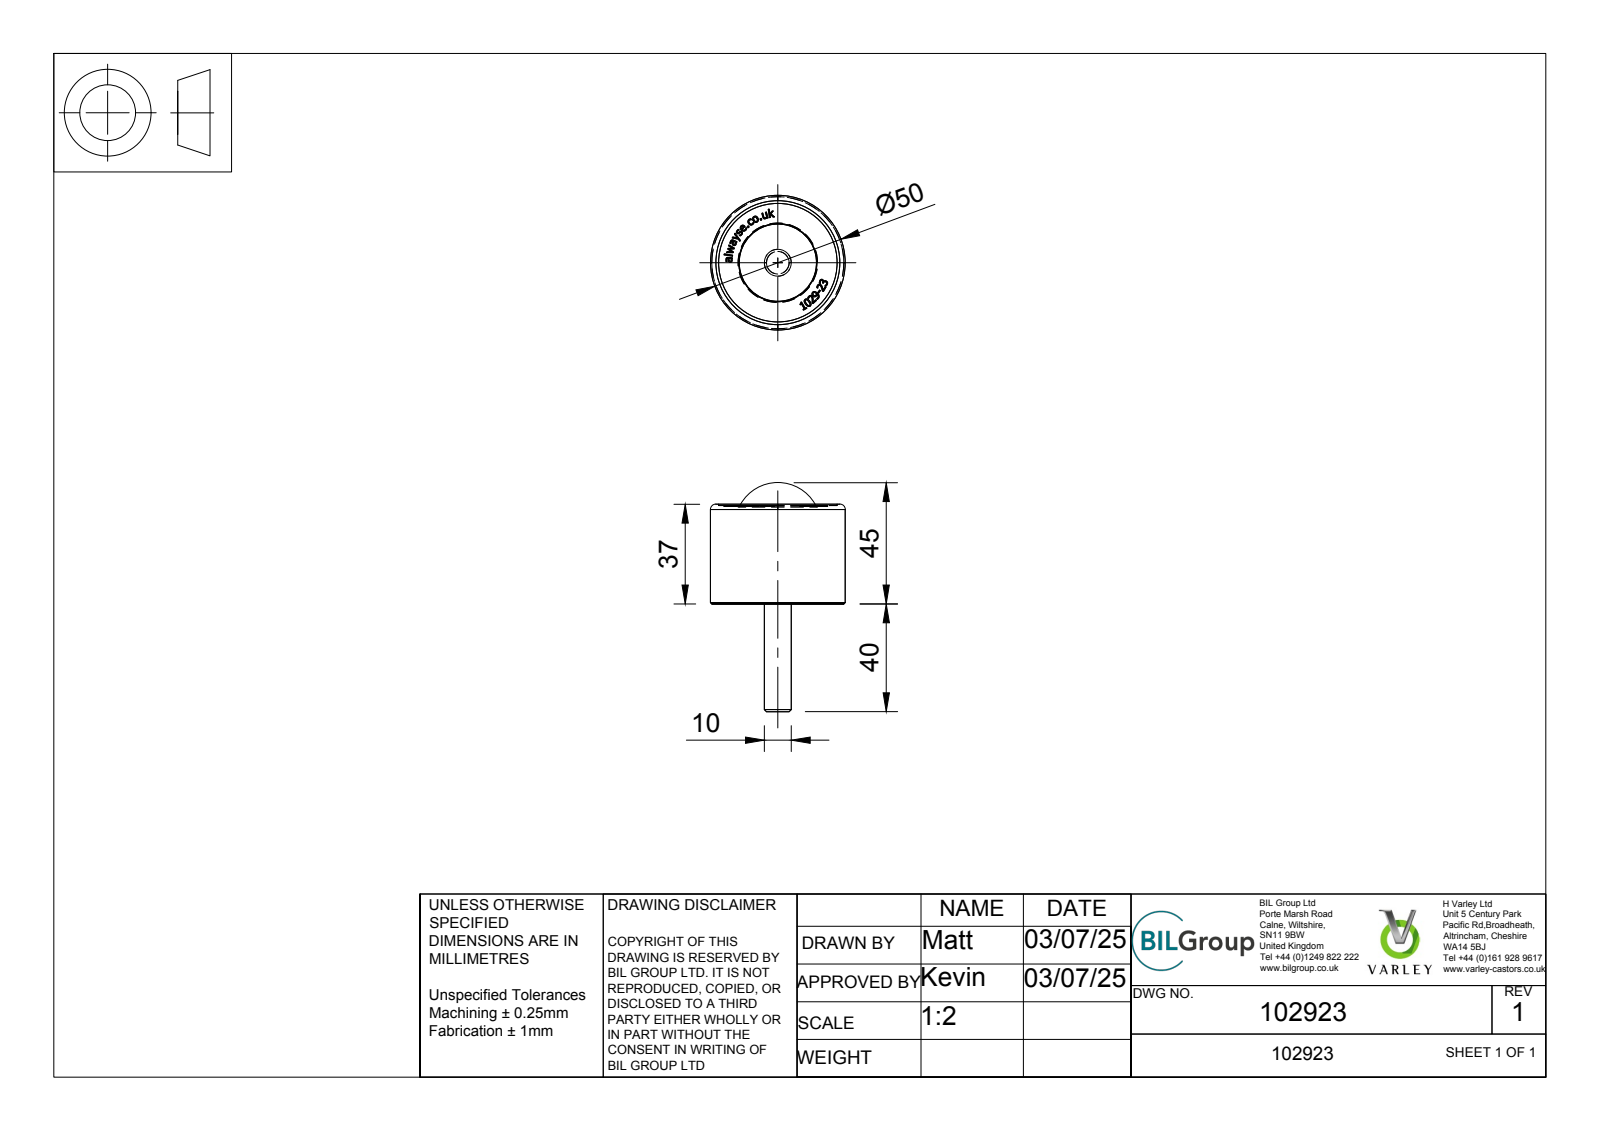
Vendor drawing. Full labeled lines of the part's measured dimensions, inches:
Part name (STEP PRODUCT): 102923 v1; 102923
STEP written by: Autodesk Translation Framework v14.10.0.0 (AUTOMOTIVE_DESIGN)
Units: inches
Bodies: 0 solids, 322 faces (147 planar, 6 cylindrical, 169 other)
Overall size (bounding box): 3.346 × 1.969 × 1.969
Round bosses / shafts (diameter × count): ⌀1.969 ×1, ⌀1.732 ×1, ⌀0.394 ×1
Main face-to-face distances: 1.437, 0.02, 1.457, 1.575, 3.012, 3.031, 0.039, 2.992, 1.417, 3
